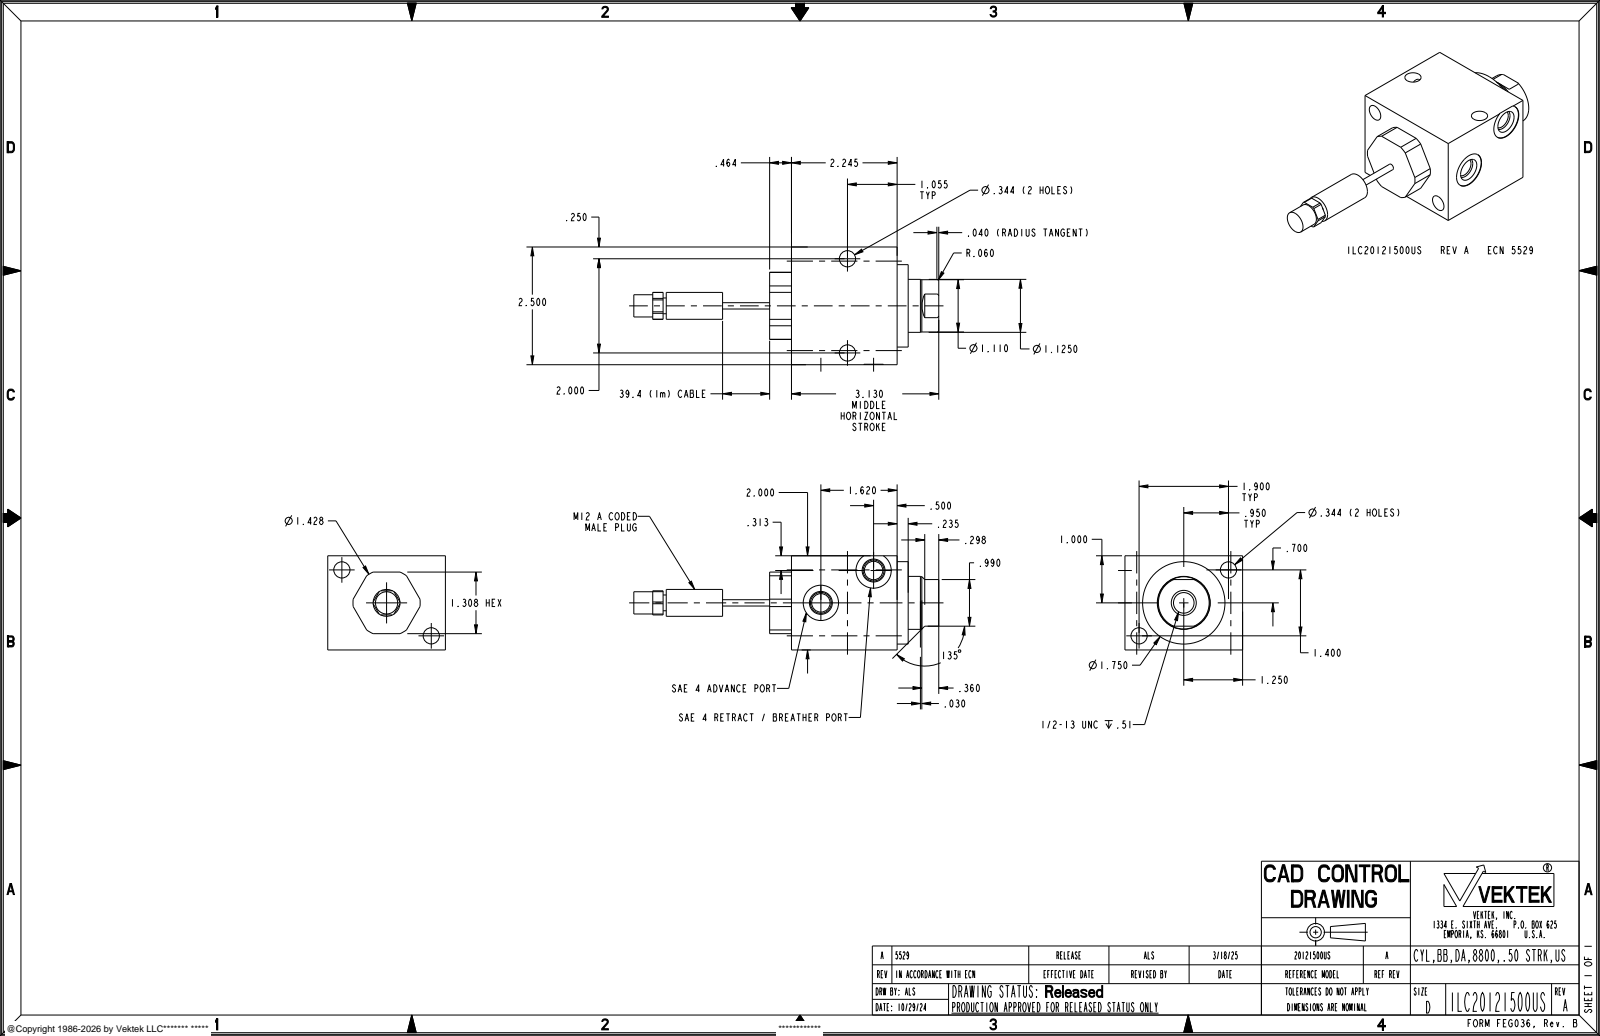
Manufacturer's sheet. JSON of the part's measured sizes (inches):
{"part_name": "ILC20121500US", "step_written_by": "CREO PARAMETRIC BY PTC INC, 2021164 (AUTOMOTIVE_DESIGN)", "units": "inches", "bodies": {"solids": 1, "faces": 99, "planar": 36, "cylindrical": 49, "other": 14}, "overall_size": [6.48, 2.75, 2], "volume_in3": 12.53, "surface_area_in2": 50.74, "round_holes": [[0.344, 4], [0.392, 2], [0.75, 2], [0.437, 1]], "round_bosses_or_shafts": [[1.75, 1], [1.125, 1], [1.11, 1], [0.571, 1], [0.5, 1], [0.472, 1], [0.335, 1], [0.134, 1]], "partial_cylinders_radius": [[0.714, 1]], "face_to_face_distances": [2, 2.5, 2.245, 2.709, 0.464, 0.235, 2.48, 2.944, 1.308, 0.65], "hole_center_spacings": [1.18, 1.314, 2, 2.36]}
